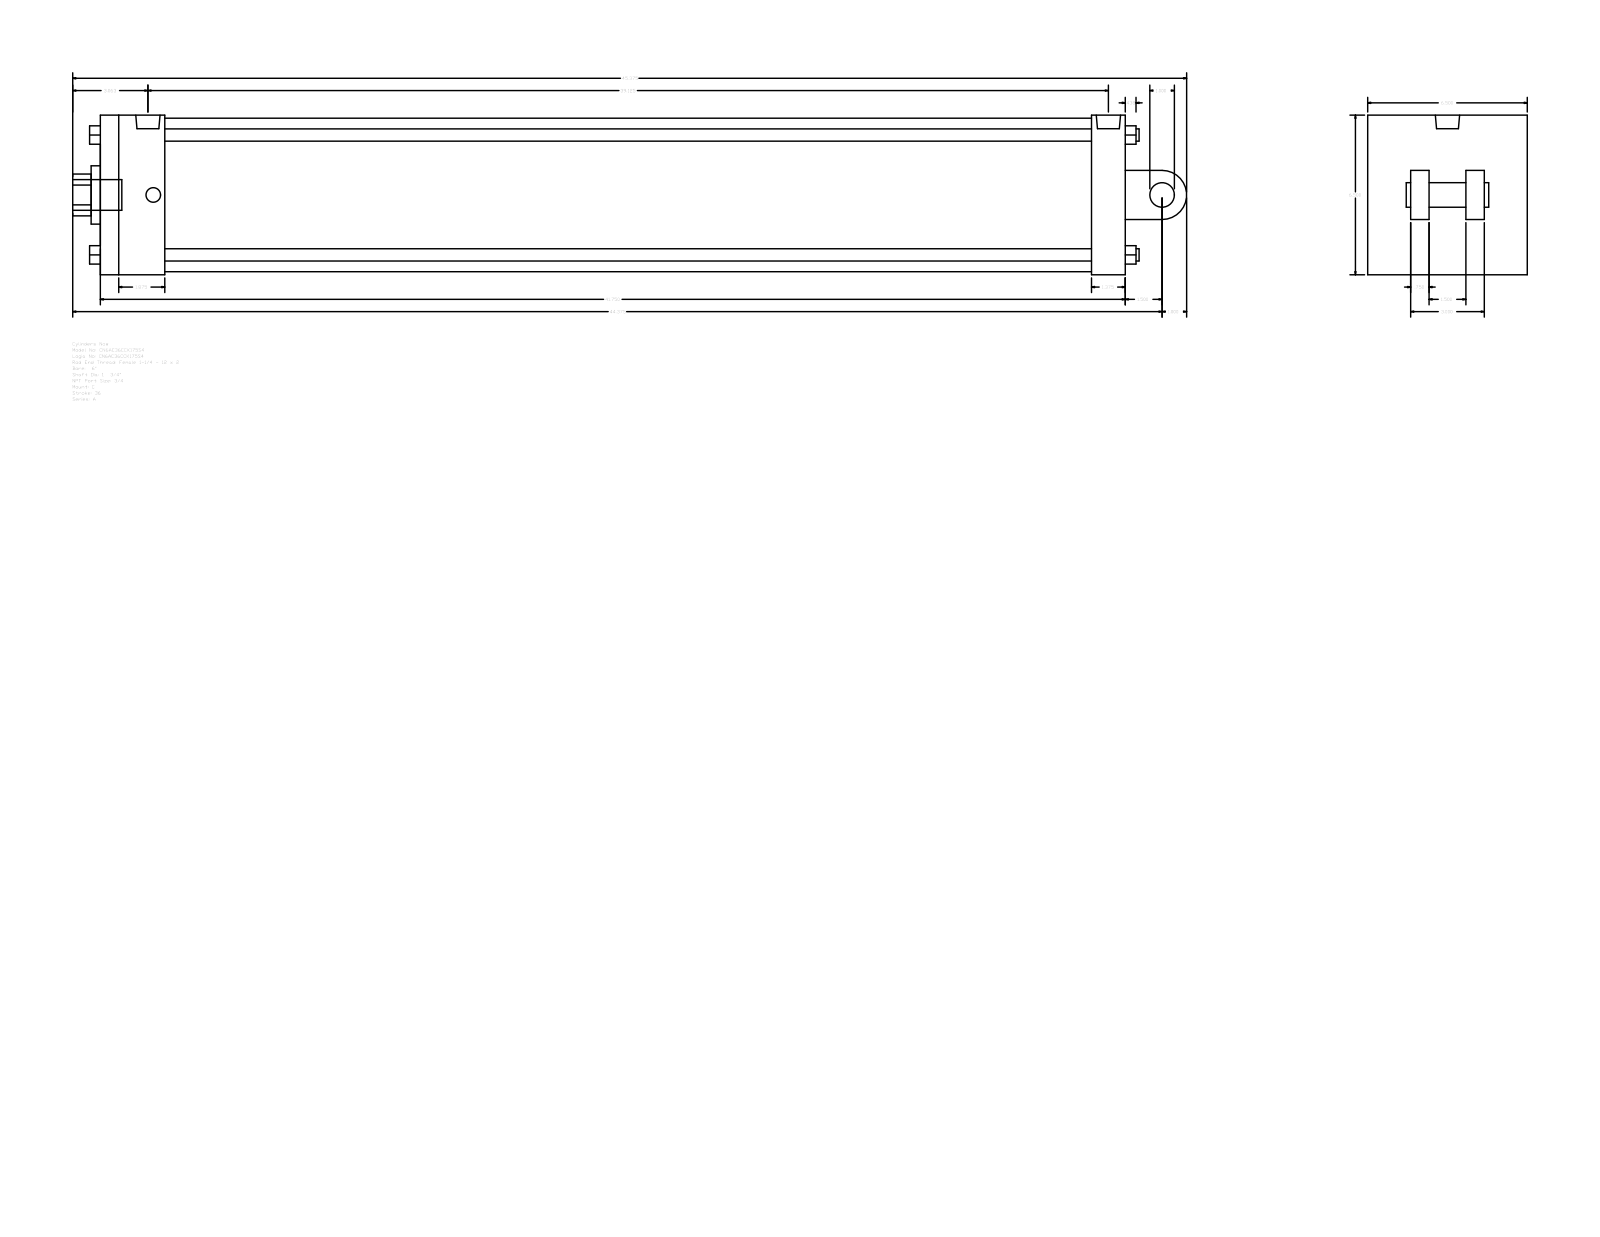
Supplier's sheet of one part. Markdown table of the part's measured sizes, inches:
| quantity | value |
| --- | --- |
| part name | A_C__0600_1.75 |
| STEP written by | GSSL Pune (CONFIG_CONTROL_DESIGN) |
| units | inches |
| bodies | 0 solids, 135 faces (102 planar, 33 cylindrical, 0 other) |
| overall size | 45.375 × 6.5 × 6.5 |
| round holes (diameter × count) | 0.594 × 2, 0.989 × 1, 1.75 × 1, 2.375 × 1, 6.25 × 1 |
| round bosses / shafts (diameter × count) | 0.5 × 4, 0.594 × 2, 1.25 × 1, 1 × 1, 0.989 × 1 |
| partial cylindrical surfaces (radius × count) | 0.852 × 1, 1 × 1 |
| main face-to-face distances | 6.5, 41.75, 0.75, 2.25, 2.625, 39.125, 40.375, 37.75, 1.375, 1.75 |
| hole center spacings | 0.219 |
